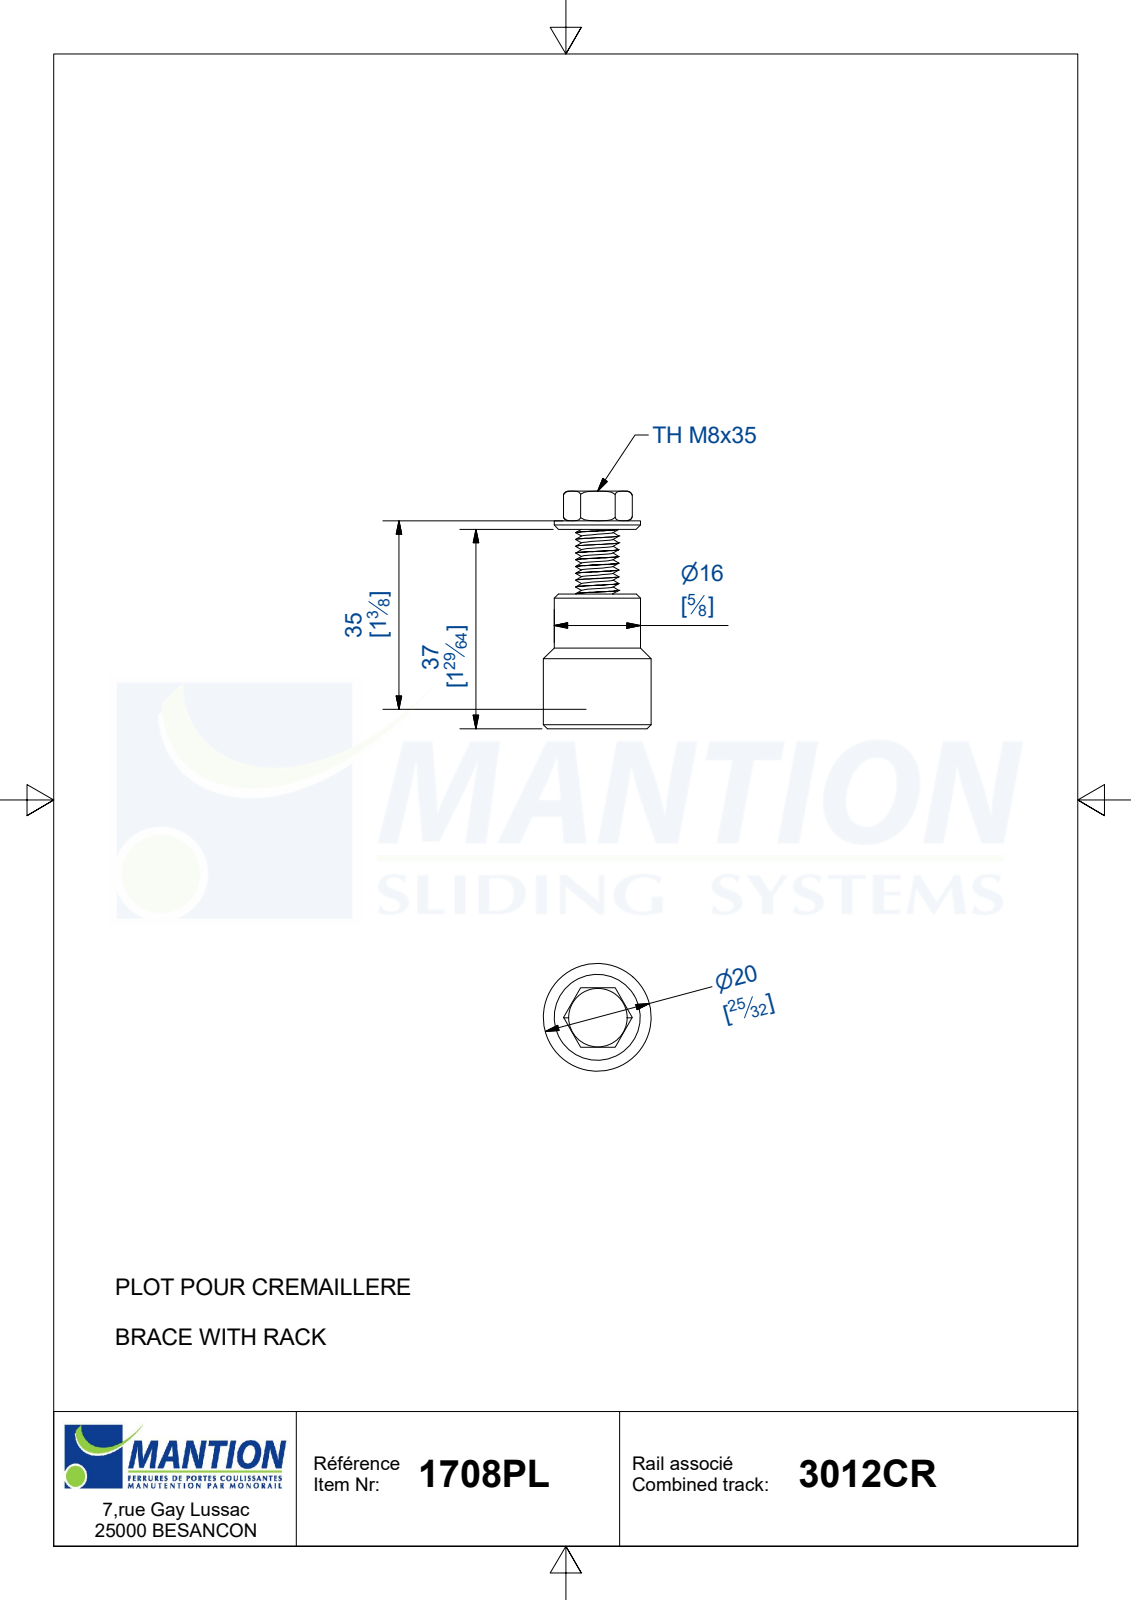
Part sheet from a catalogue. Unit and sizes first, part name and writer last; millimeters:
Units: millimetres
Overall size (bounding box): 44.1 × 20 × 20
Round holes (diameter × count): ⌀8.4 ×1, ⌀8.6 ×1
Round bosses / shafts (diameter × count): ⌀20 ×1, ⌀16 ×1, ⌀8 ×1
Main face-to-face distances: 38.6, 1.6, 37, 11, 5.5, 7.1, 44.1, 19.1, 13.6, 12
Volume: 7 238 mm³ · Surface area: 4 780 mm²
Bodies: 3 solids, 90 faces (14 planar, 61 cylindrical, 15 other)
Part name (STEP PRODUCT): 1708PL; local.ISO.63.30.1; vis TH M8x35
STEP written by: Autodesk Inventor 2017 (AUTOMOTIVE_DESIGN)
